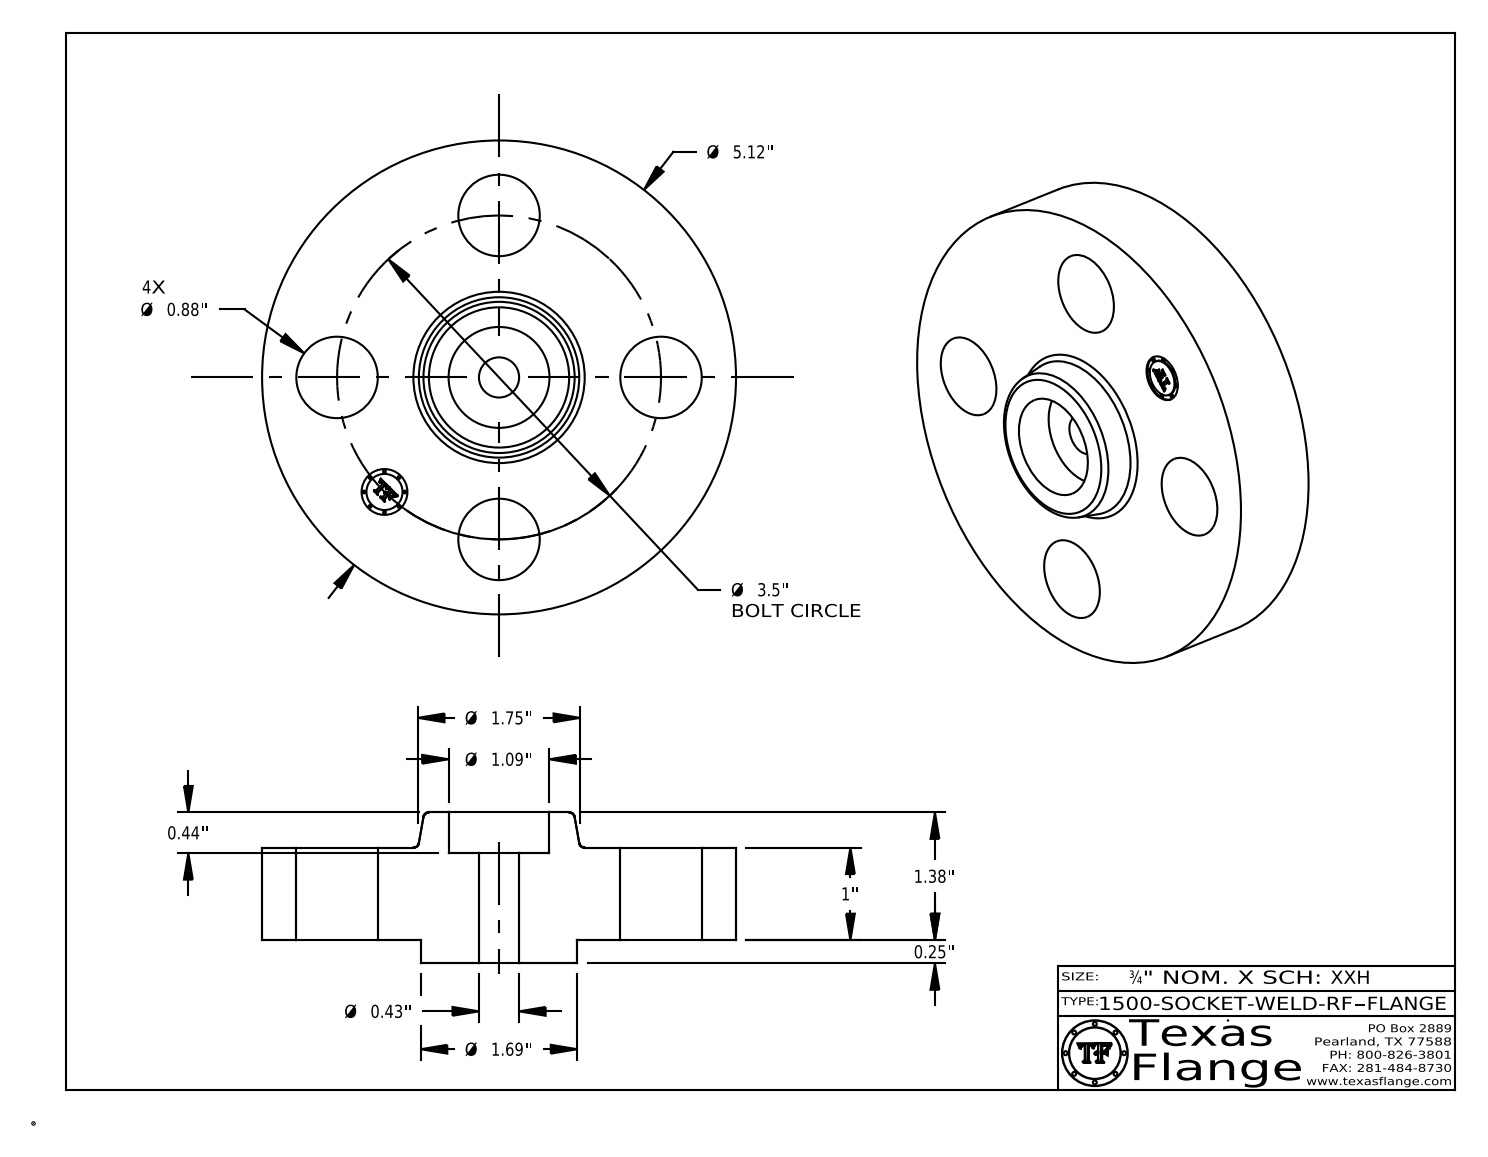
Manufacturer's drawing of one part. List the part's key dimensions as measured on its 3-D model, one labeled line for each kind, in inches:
Part name (STEP PRODUCT): 1500-SOCKET-WELD-RF
STEP written by: CATIA V5 STEP AP214 (AUTOMOTIVE_DESIGN)
Units: inches
Bodies: 1 solid, 412 faces (370 planar, 36 cylindrical, 6 other)
Overall size (bounding box): 5.12 × 5.12 × 1.63
Volume: 18.97 in³ · Surface area: 69.22 in²
Round holes (diameter × count): ⌀0.88 ×4, ⌀0.434 ×1, ⌀0.495 ×1, ⌀1.09 ×1
Round bosses / shafts (diameter × count): ⌀0.03 ×8, ⌀5.12 ×1, ⌀1.69 ×1, ⌀0.39 ×1
Main face-to-face distances: 1, 0.25, 1.25, 1.63, 1.38, 0.38, 0.06, 1.19, 0.94, 0.44
Hole centre spacings: 1.75, 2.475, 1.339, 3.233, 3.5
